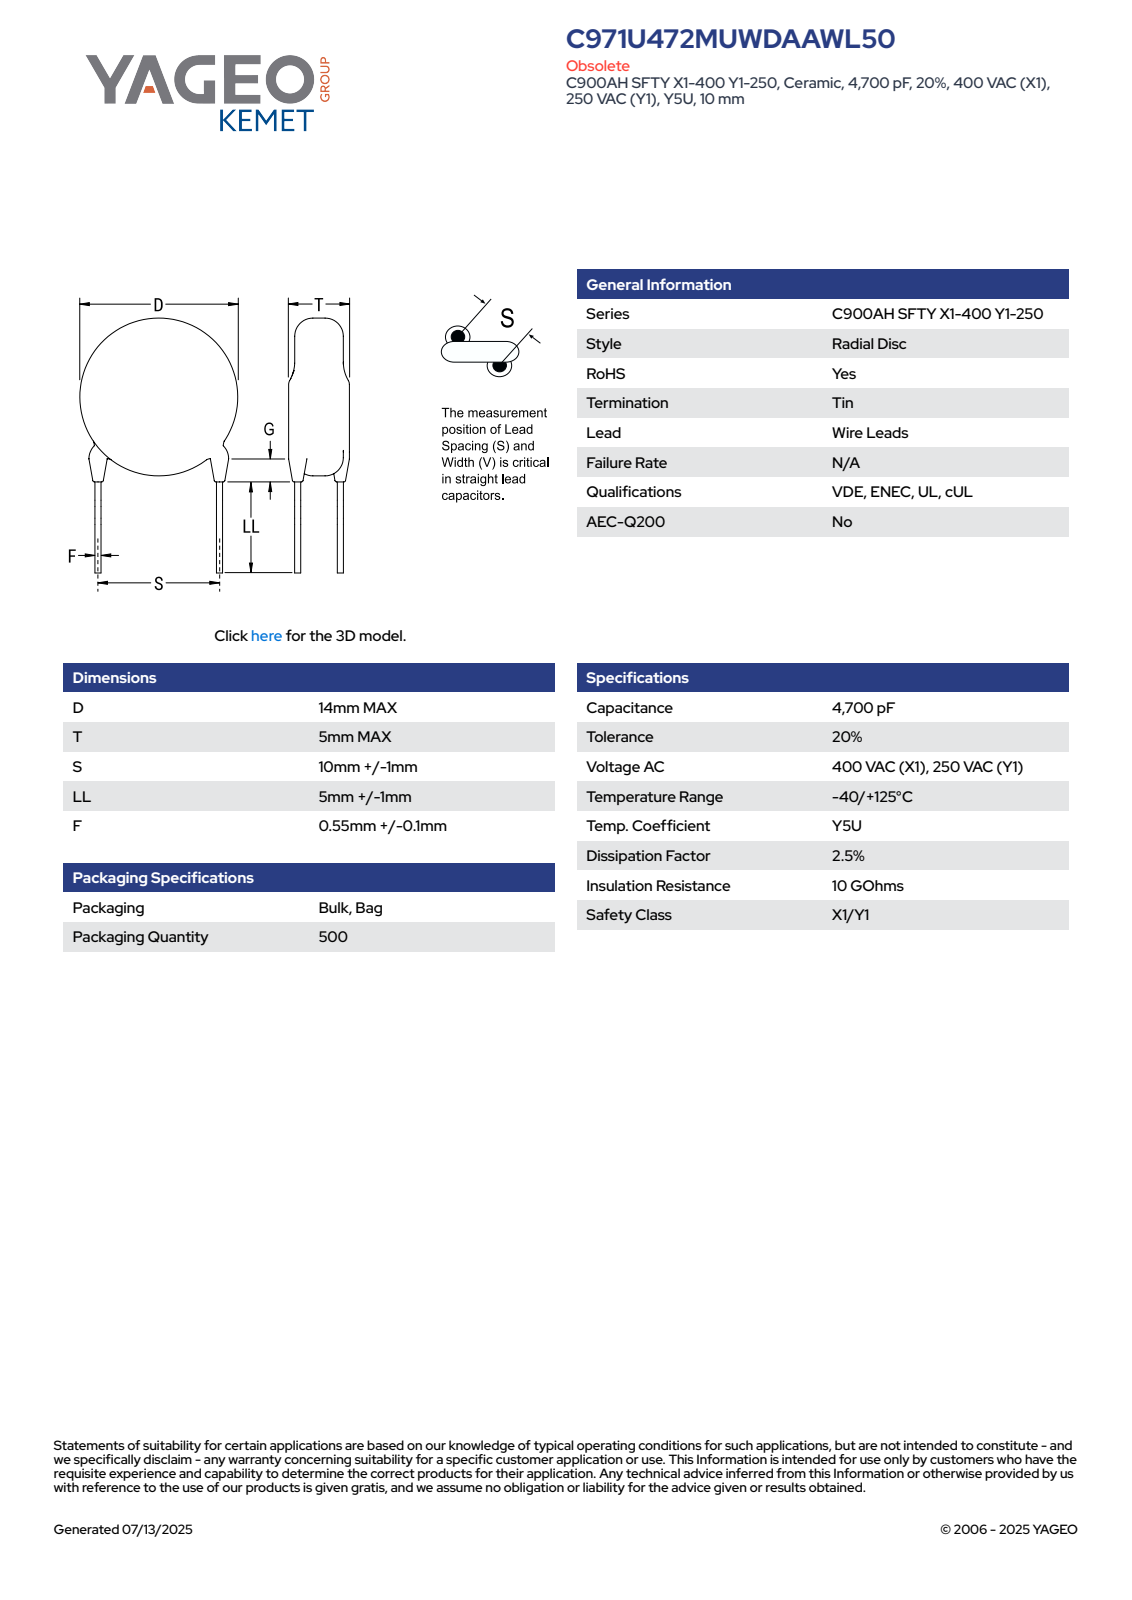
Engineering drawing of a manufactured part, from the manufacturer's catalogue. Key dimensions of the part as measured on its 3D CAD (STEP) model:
Part name (STEP PRODUCT): CCD_STC900_D14T5S10LL6F0.65G3
STEP written by: SolidWorks 2014 (AUTOMOTIVE_DESIGN)
Units: millimetres
Bodies: 4 solids, 83 faces (61 planar, 6 cylindrical, 16 other)
Overall size (bounding box): 20.29 × 14 × 5
Volume: 758 mm³ · Surface area: 539 mm²
Round bosses / shafts (diameter × count): ⌀0.65 ×2, ⌀14 ×1
Main face-to-face distances: 5, 14.09, 12.48, 1.61, 0.4, 6.61, 0.44, 0.6, 0.31, 1.3
